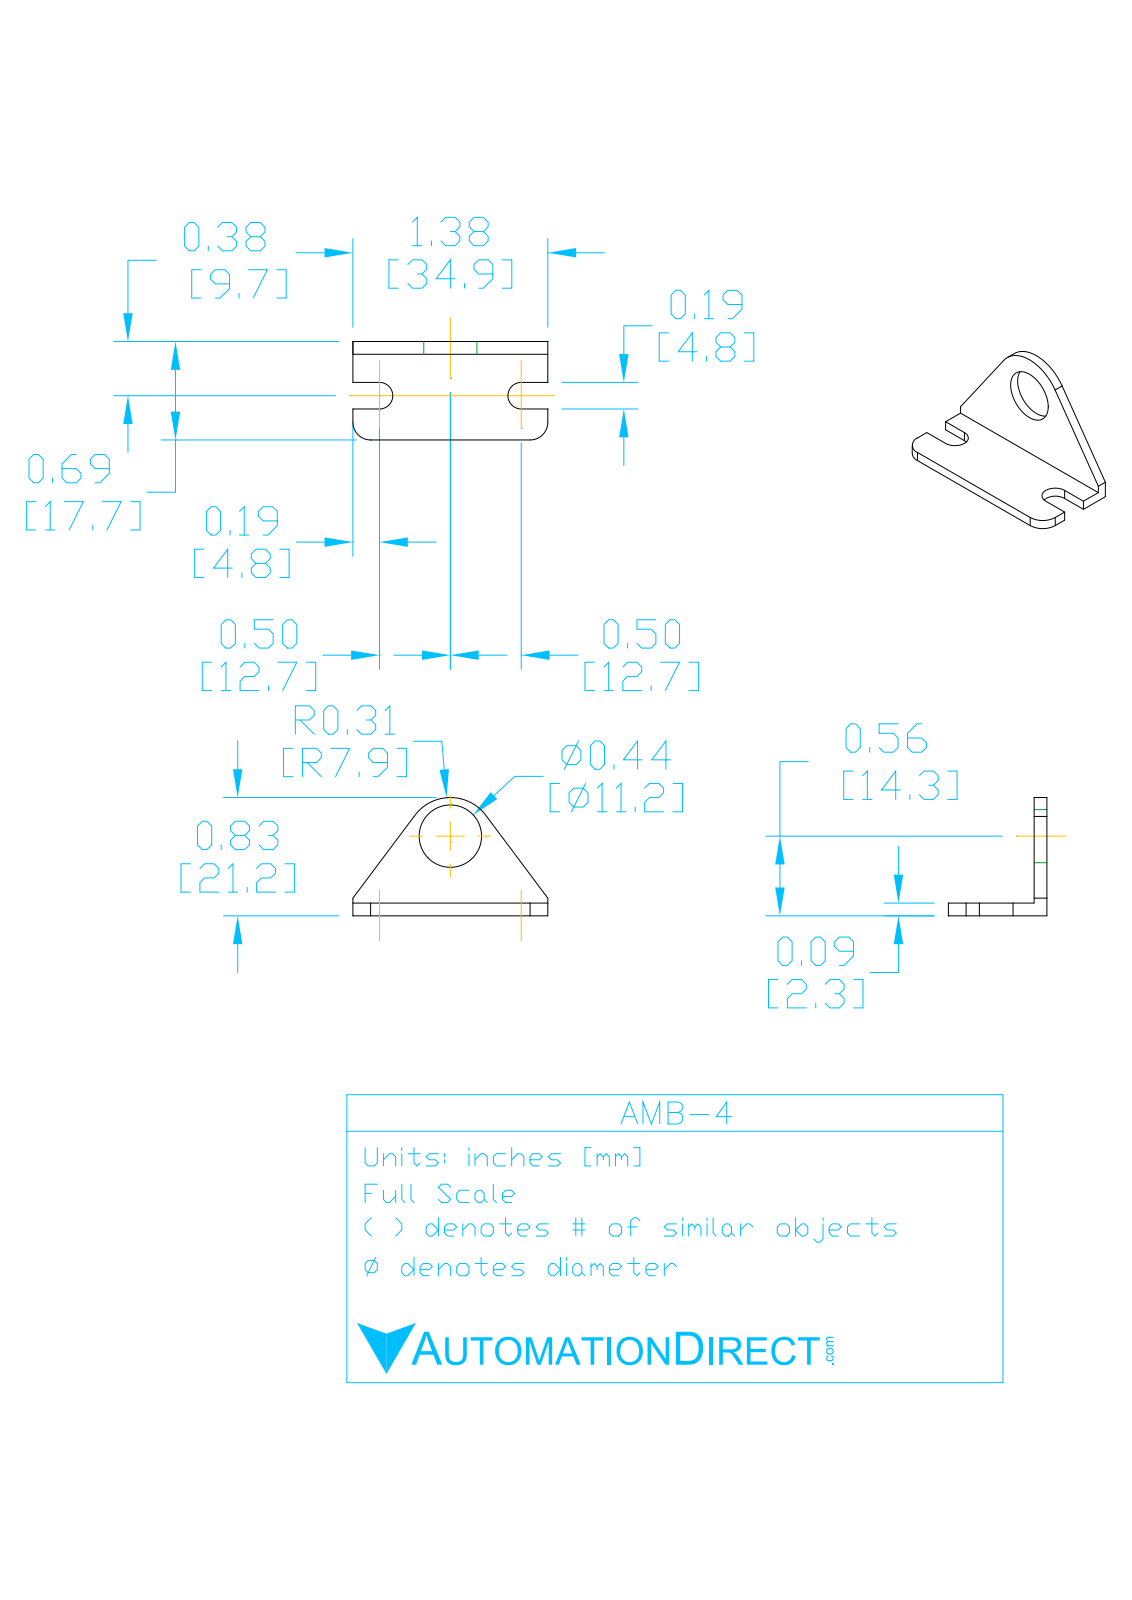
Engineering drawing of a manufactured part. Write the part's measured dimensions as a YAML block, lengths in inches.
part_name: "AMB-4"
step_written_by: "SolidWorks 2017 (AUTOMOTIVE_DESIGN)"
units: inches
bodies: {solids: 1, faces: 28, planar: 19, cylindrical: 9, other: 0}
overall_size: [1.375, 0.835, 0.687]
volume: 0.116
surface_area: 3.203
round_holes:
  - {diameter: 0.437, count: 1}
partial_cylinders:
  - {radius: 0.094, count: 2}
  - {radius: 0.125, count: 2}
  - {radius: 0.03, count: 1}
  - {radius: 0.121, count: 1}
  - {radius: 0.31, count: 1}
face_to_face_distances: [0.091, 0.597, 0.687, 1.375, 0.407, 0.19, 0.281, 0.218, 0.189, 0.379]
